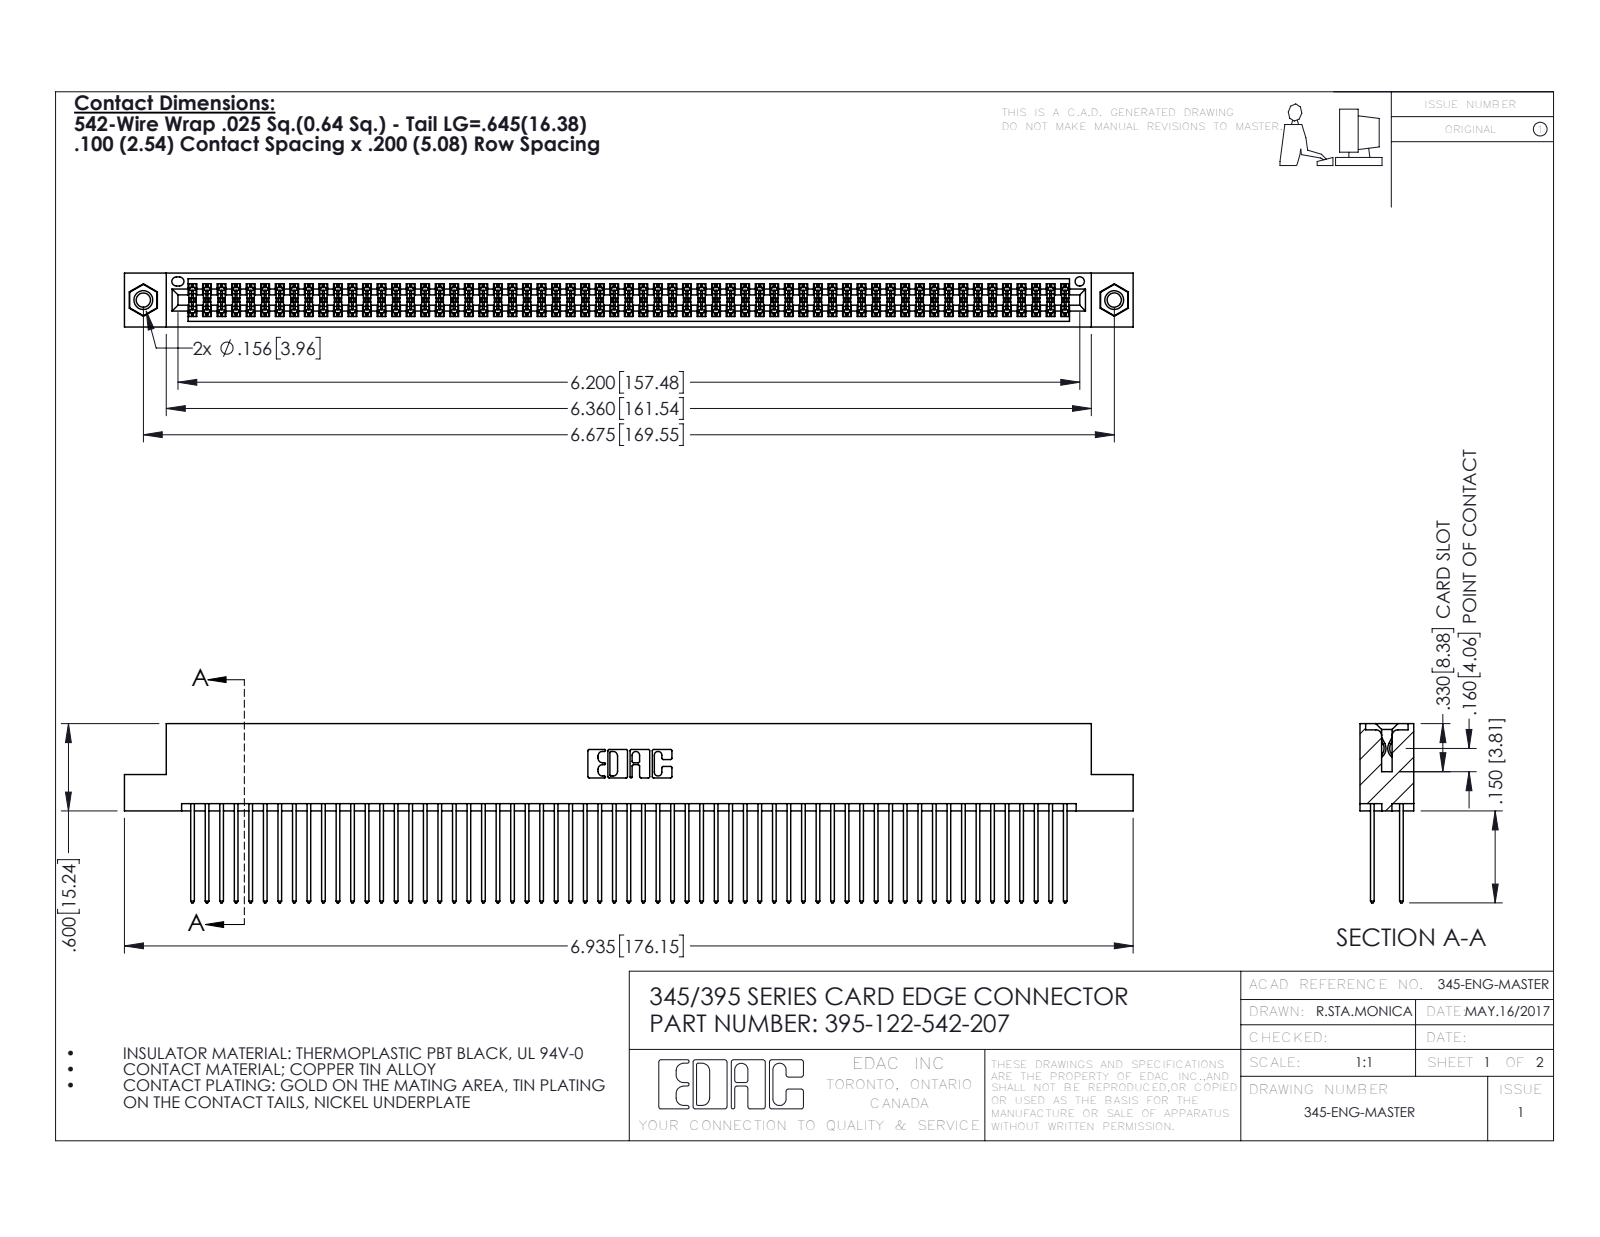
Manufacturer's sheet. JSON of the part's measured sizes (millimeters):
{"part_name": "345-292-001_345-293-142; 345 Part_Flush Mounting Lugs - 0.156 Dia-TI; 345-250-001_345-250-005-103; 395-122-542-207", "step_written_by": "SolidWorks 2016 (CONFIG_CONTROL_DESIGN)", "units": "millimeters", "bodies": {"solids": 125, "faces": 6286, "planar": 4138, "cylindrical": 2132, "other": 16}, "overall_size": [176.1, 31.3, 9.4], "volume_mm3": 17850, "surface_area_mm2": 29430, "round_holes": [[2.5, 2], [3.2, 2], [4, 2], [1.6, 1]], "round_bosses_or_shafts": [[3.9, 2]], "partial_cylinders_radius": [[0.2, 183], [0.3, 122], [0.3, 22], [0.2, 6], [0.8, 6], [0.7, 3], [0.4, 2], [0.5, 2]], "face_to_face_distances": [1.8, 7.6, 5.1, 2.5, 6.9, 0.6, 5.7, 9.4, 4.4, 3.8], "hole_center_spacings": [6.9, 163.6, 169.5]}
